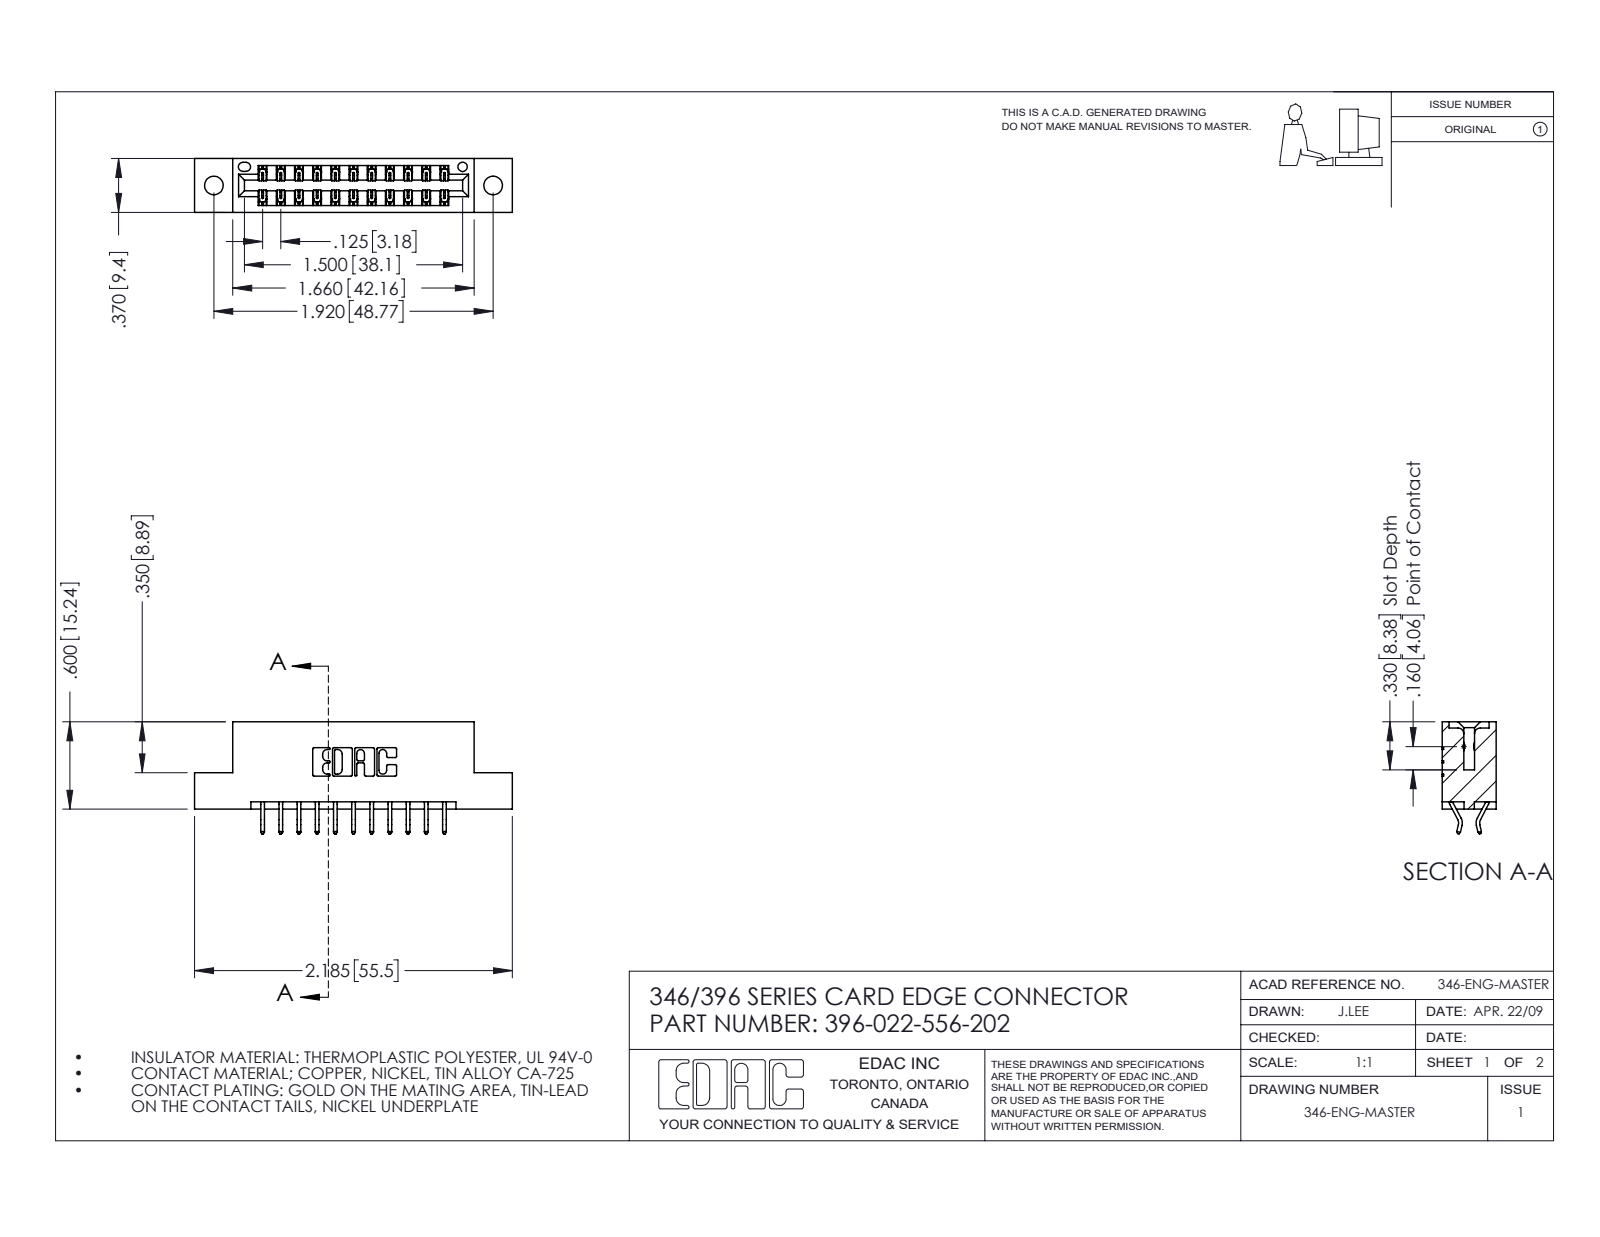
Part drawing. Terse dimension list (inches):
name: 345-292-001_556 Tail; 346 Part_Flush Mounting Lugs - 0.128 Dia; 396-022-556-202
written by: SolidWorks 2016 (CONFIG_CONTROL_DESIGN)
unit: in
bodies: 23 solids, 1398 faces (934 planar, 464 cylindrical, 0 other)
size: 2.185 × 0.77 × 0.37
volume: 0.313 in³; area: 9.733 in²
holes: 2× ⌀0.128, 1× ⌀0.064
rounds: 33× R0.006, 22× R0.01, 6× R0.007, 6× R0.031, 3× R0.026, 2× R0.01, 2× R0.014, 2× R0.022
face distances: 0.25, 0.048, 0.322, 0.37, 0.025, 0.072, 0.298, 0.275, 0.148, 0.222
hole spacings: 0.246, 1.715, 1.92
